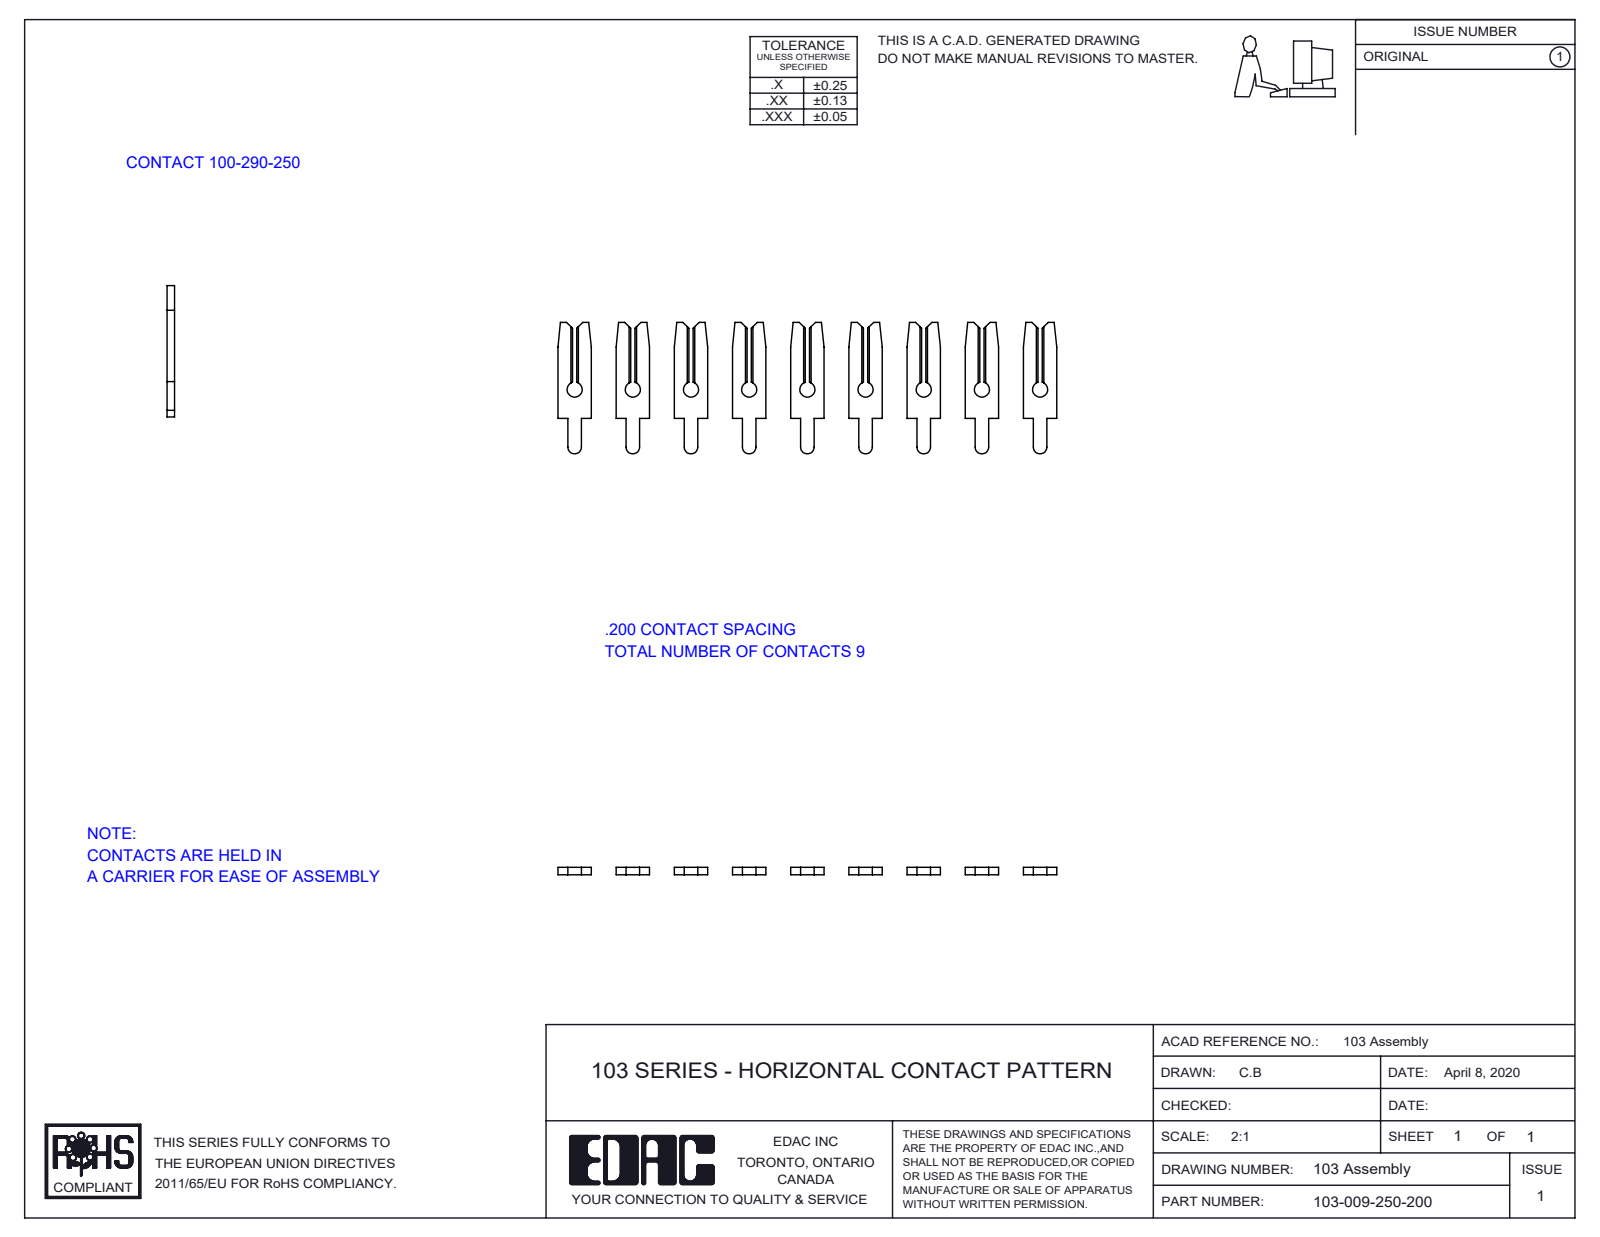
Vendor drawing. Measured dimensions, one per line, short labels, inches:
name: 103-009-250-200; 100-290-001_100-290-250
written by: SolidWorks 2016 (CONFIG_CONTROL_DESIGN)
unit: in
bodies: 9 solids, 216 faces (180 planar, 36 cylindrical, 0 other)
size: 1.715 × 0.452 × 0.026
volume: 0.009 in³; area: 1.023 in²
holes: 9× ⌀0.052
rounds: 9× R0.024
face distances: 0.026, 0.2, 0.4, 0.6, 0.8, 0.115, 0.315, 1, 0.085, 0.141
hole spacings: 0.2, 0.4, 0.6, 0.8, 1, 1.2, 1.4, 1.6
